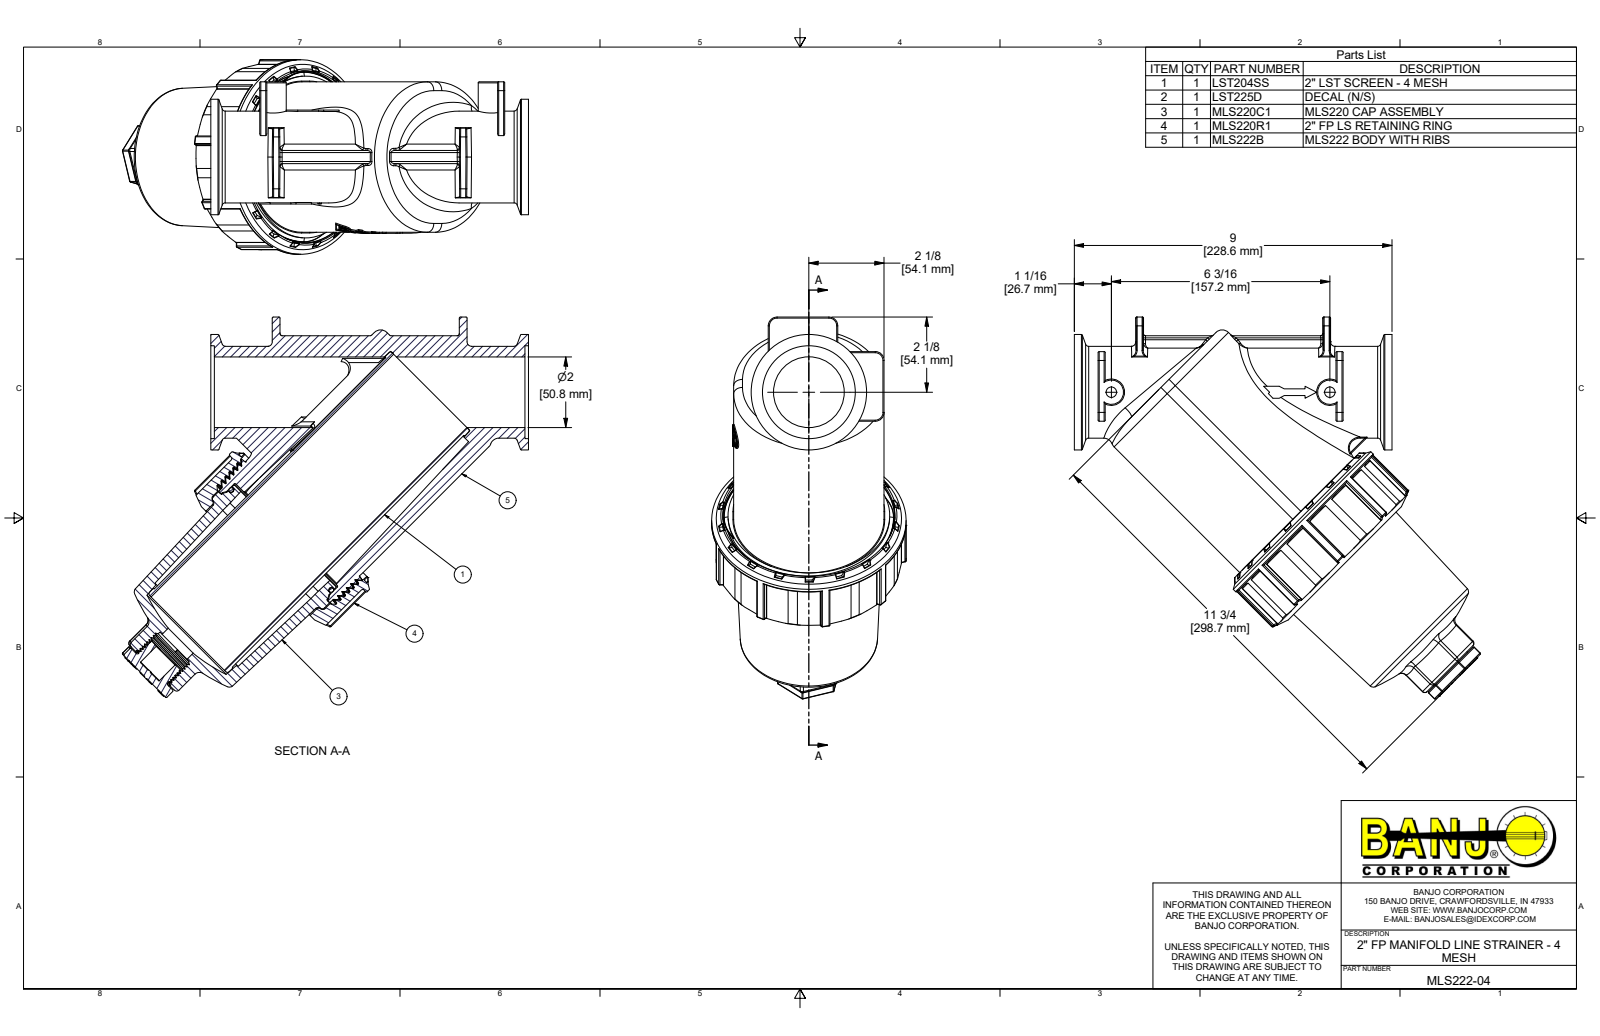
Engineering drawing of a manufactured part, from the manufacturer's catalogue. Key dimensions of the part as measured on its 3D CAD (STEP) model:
Part name (STEP PRODUCT): MLS222-04; MLS222B; MLS220C1; MLS220C1X (+5 more)
STEP written by: Autodesk Inventor 2019 (AUTOMOTIVE_DESIGN)
Units: inches
Bodies: 7 solids, 1884 faces (784 planar, 345 cylindrical, 755 other)
Overall size (bounding box): 11.507 × 10.817 × 5.51
Volume: 90.38 in³ · Surface area: 738 in²
Round holes (diameter × count): ⌀0.295 ×2, ⌀0.454 ×1, ⌀0.641 ×1, ⌀0.75 ×1, ⌀1 ×1, ⌀1.176 ×1, ⌀2 ×1, ⌀2.63 ×1, ⌀2.937 ×1, ⌀3.53 ×1, ⌀4.13 ×1, ⌀4.175 ×1
Round bosses / shafts (diameter × count): ⌀3.188 ×2, ⌀5.51 ×1, ⌀5.25 ×1, ⌀4.45 ×1, ⌀4.215 ×1, ⌀4.1 ×1, ⌀3.905 ×1, ⌀3.27 ×1
Partial cylindrical surfaces — rounded edges, fillets, slot ends (radius × count): R0.03 ×76, R0.01 ×36, R0.06 ×12, R0.09 ×12, R0.25 ×8, R0.125 ×6, R0.02 ×2, R0.039 ×2
Main face-to-face distances: 0.1, 8.9, 0.3, 9, 5.809, 6.109, 5.3, 0.2, 6.74, 1.096
Hole centre spacings: 2.522, 4.191, 6.19
